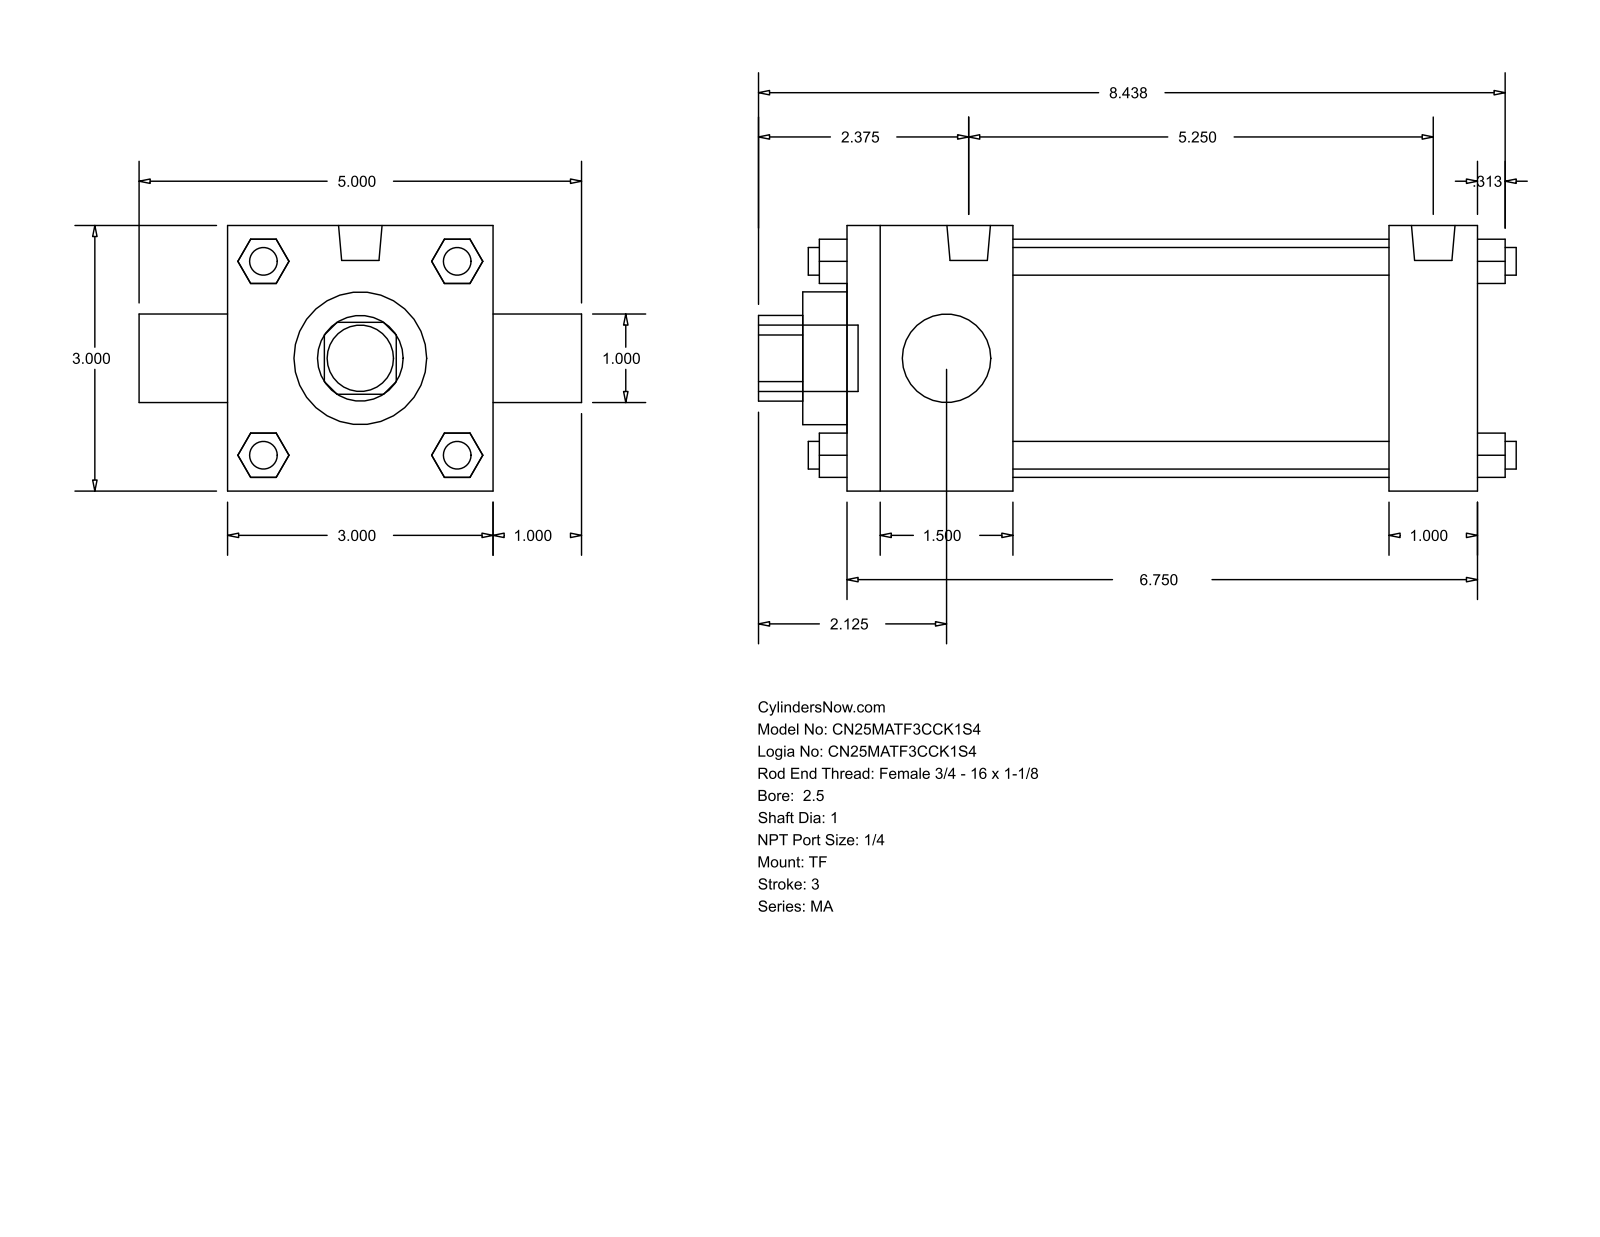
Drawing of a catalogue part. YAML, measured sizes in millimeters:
part_name: "MA_TF__0250_1"
step_written_by: "GSSL Pune (CONFIG_CONTROL_DESIGN)"
units: millimeters
bodies: {solids: 0, faces: 120, planar: 92, cylindrical: 28, other: 0}
overall_size: [217.49, 127, 76.2]
round_holes:
  - {diameter: 25.4, count: 2}
  - {diameter: 38.1, count: 1}
  - {diameter: 68.33, count: 1}
round_bosses_or_shafts:
  - {diameter: 7.94, count: 7}
  - {diameter: 12.49, count: 2}
  - {diameter: 19.05, count: 1}
partial_cylinders:
  - {radius: 12.29, count: 1}
face_to_face_distances: [76.2, 180.98, 12.7, 47.63, 155.57, 107.94, 133.35, 25.41, 25.4, 101.6]
